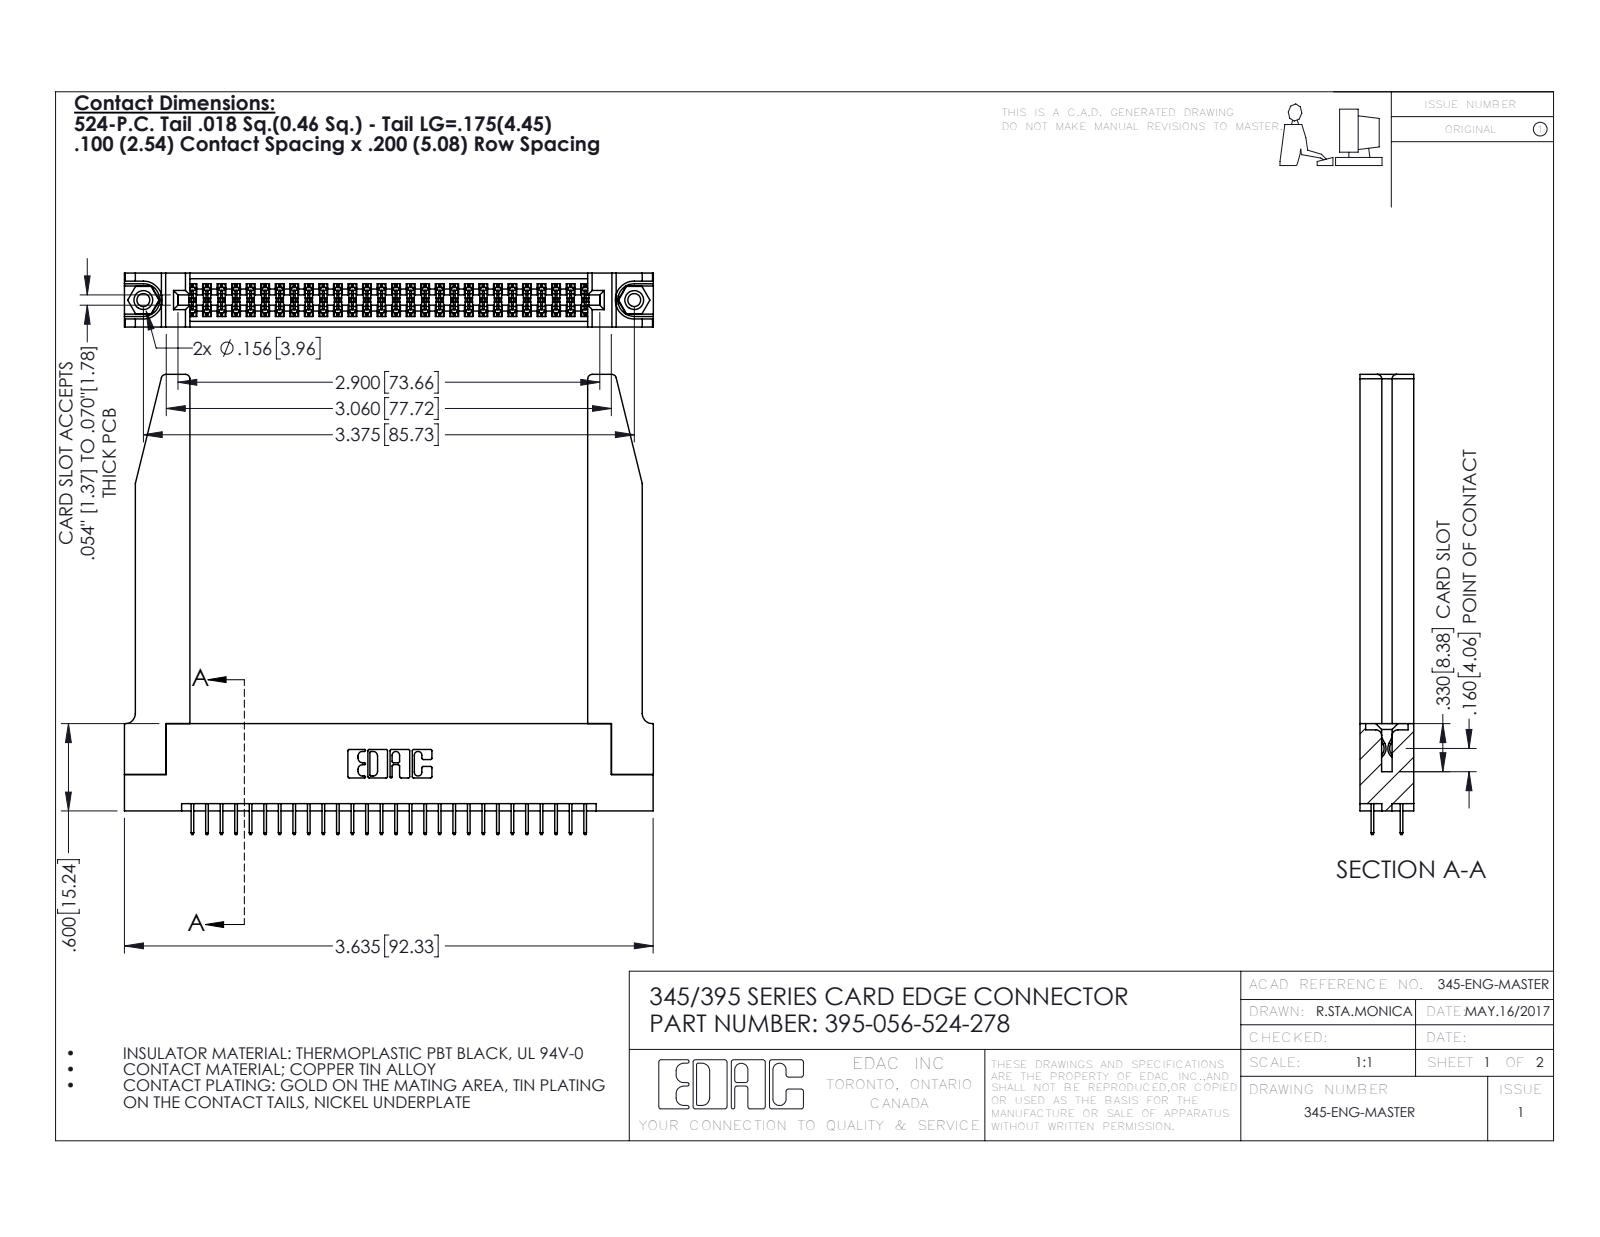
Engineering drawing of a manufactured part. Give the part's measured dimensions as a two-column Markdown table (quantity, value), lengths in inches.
| quantity | value |
| --- | --- |
| part name | 345-292-001_345-293-124; 395-056-524-278; 345-220-078_345-220-078; 345-250-001_345-250-001-102 (+1 more) |
| STEP written by | SolidWorks 2016 (CONFIG_CONTROL_DESIGN) |
| units | inches |
| bodies | 61 solids, 3384 faces (2406 planar, 926 cylindrical, 52 other) |
| overall size | 3.636 × 3.162 × 0.37 |
| volume | 1.009 in³ |
| surface area | 29.9 in² |
| round holes (diameter × count) | 0.089 × 2, 0.125 × 2, 0.156 × 2, 0.064 × 1 |
| round bosses / shafts (diameter × count) | 0.155 × 2 |
| partial cylindrical surfaces (radius × count) | 0.006 × 84, 0.01 × 22, 0.03 × 8, 0.007 × 6, 0.031 × 6, 0.026 × 3, 0.014 × 2, 0.019 × 2 |
| main face-to-face distances | 0.37, 0.072, 0.298, 0.2, 0.098, 0.272, 0.025, 0.225, 0.148, 0.15 |
| hole center spacings | 0.27, 3.14, 3.375 |
